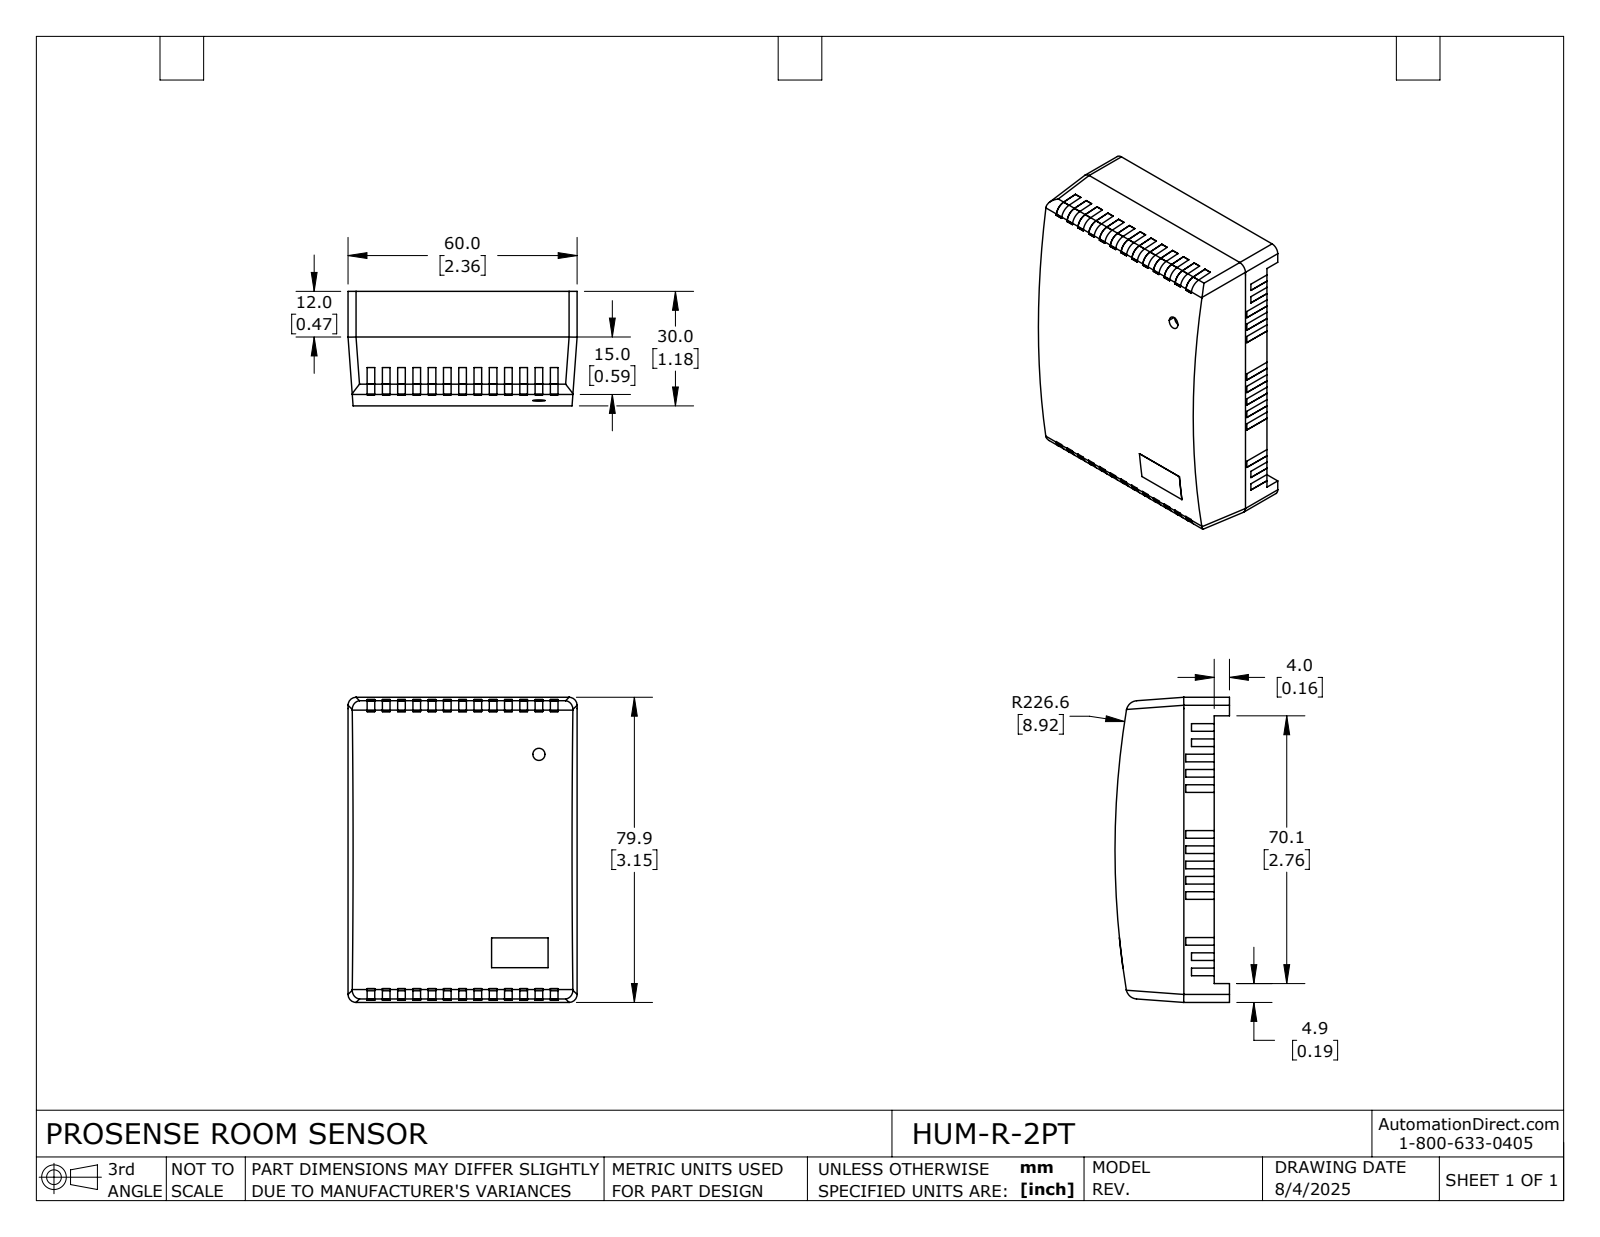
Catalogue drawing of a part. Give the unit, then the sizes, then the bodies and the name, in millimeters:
Units: millimetres
Overall size (bounding box): 79.9 × 60 × 30
Partial cylindrical surfaces — rounded edges, fillets, slot ends (radius × count): R2.1 ×8, R226.5 ×3, R2.1 ×2, R2.9 ×2, R2.9 ×2, R226.5 ×1
Main face-to-face distances: 79.9, 4, 60, 60, 24.3, 20.3, 4.9, 75, 70.1, 75
Volume: 118 400 mm³ · Surface area: 17 070 mm²
Bodies: 1 solid, 461 faces (354 planar, 105 cylindrical, 2 other)
Part name (STEP PRODUCT): HUM-R-PT
STEP written by: SolidWorks 2024 (AUTOMOTIVE_DESIGN)
